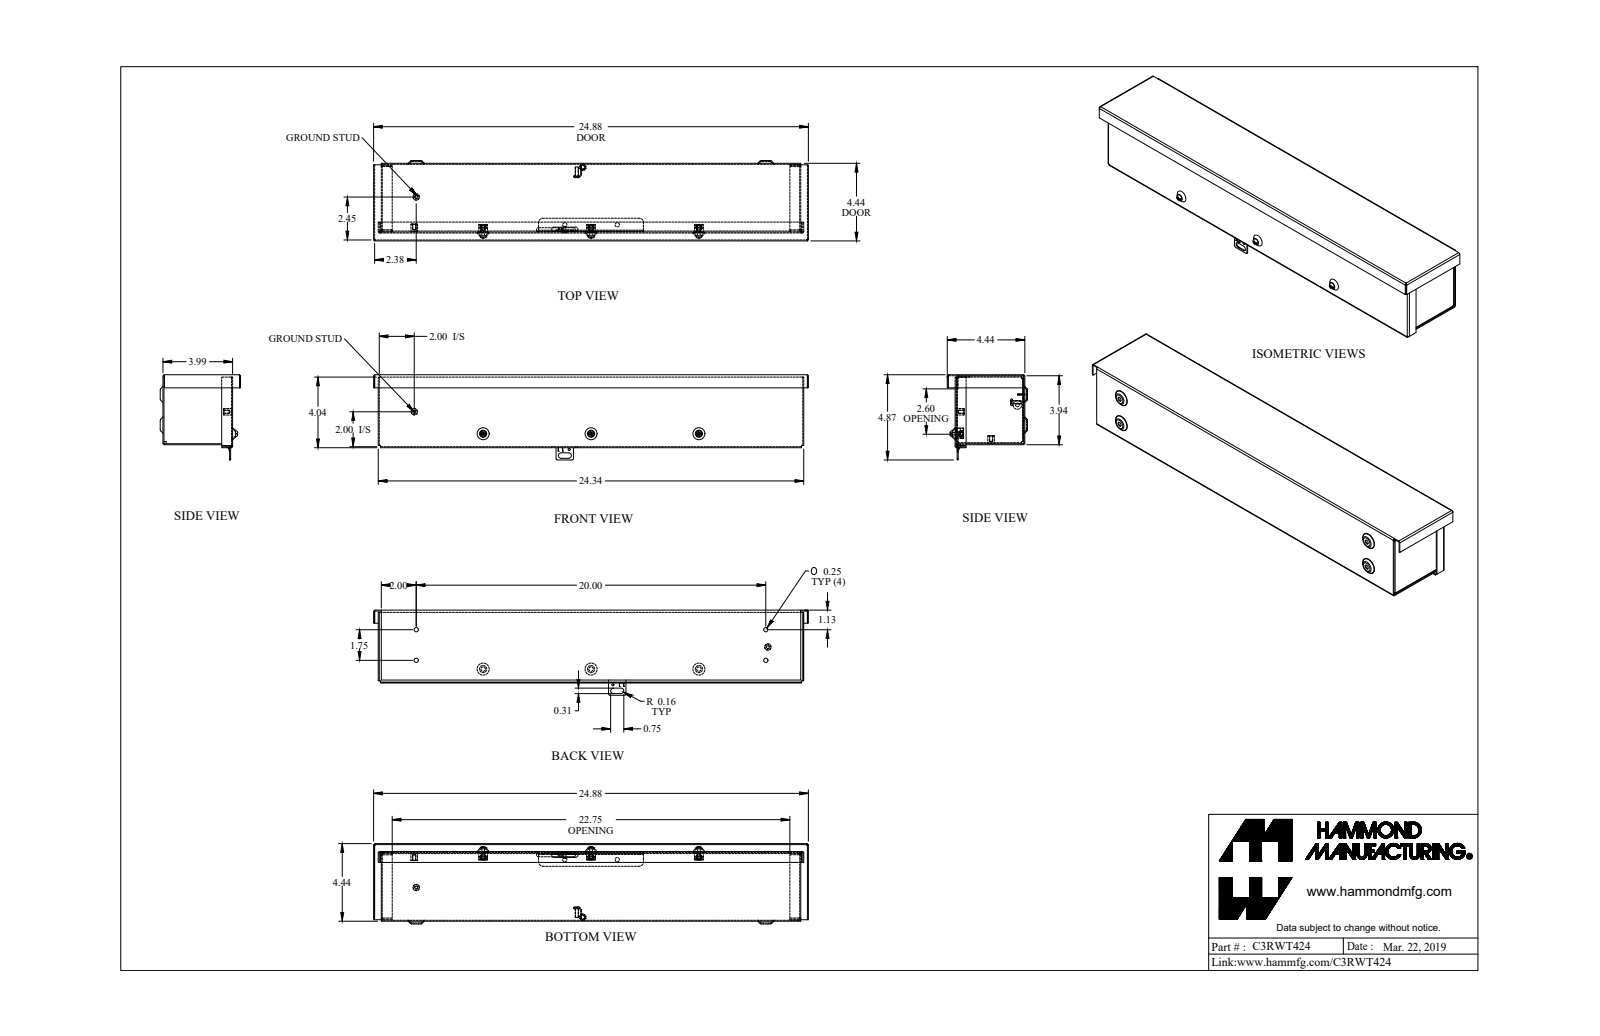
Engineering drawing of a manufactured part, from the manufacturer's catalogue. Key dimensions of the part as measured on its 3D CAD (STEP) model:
Part name (STEP PRODUCT): C3RWT424_Default
STEP written by: SolidWorks 2019 (CONFIG_CONTROL_DESIGN)
Units: inches
Bodies: 22 solids, 766 faces (415 planar, 239 cylindrical, 112 other)
Overall size (bounding box): 24.875 × 4.871 × 4.594
Volume: 29.56 in³ · Surface area: 1 047 in²
Round holes (diameter × count): ⌀0.25 ×6, ⌀0.156 ×5, ⌀0.214 ×3, ⌀0.23 ×3, ⌀0.203 ×2, ⌀0.125 ×1, ⌀0.137 ×1, ⌀0.2 ×1, ⌀0.215 ×1
Round bosses / shafts (diameter × count): ⌀0.19 ×4, ⌀0.148 ×3, ⌀0.375 ×2, ⌀0.5 ×1, ⌀0.367 ×1, ⌀0.21 ×1, ⌀0.152 ×1, ⌀0.125 ×1
Partial cylindrical surfaces — rounded edges, fillets, slot ends (radius × count): R0.029 ×18, R0.086 ×18, R0.125 ×13, R0.08 ×12, R0.108 ×12, R0.022 ×6, R0.25 ×6, R0.016 ×4
Main face-to-face distances: 0.057, 3.943, 3.928, 3.871, 3.886, 4, 3.985, 0.172, 4.381, 0.51
Hole centre spacings: 3.578, 16.554, 1.421, 1.75, 3.86, 4.44, 6.172, 6.674
